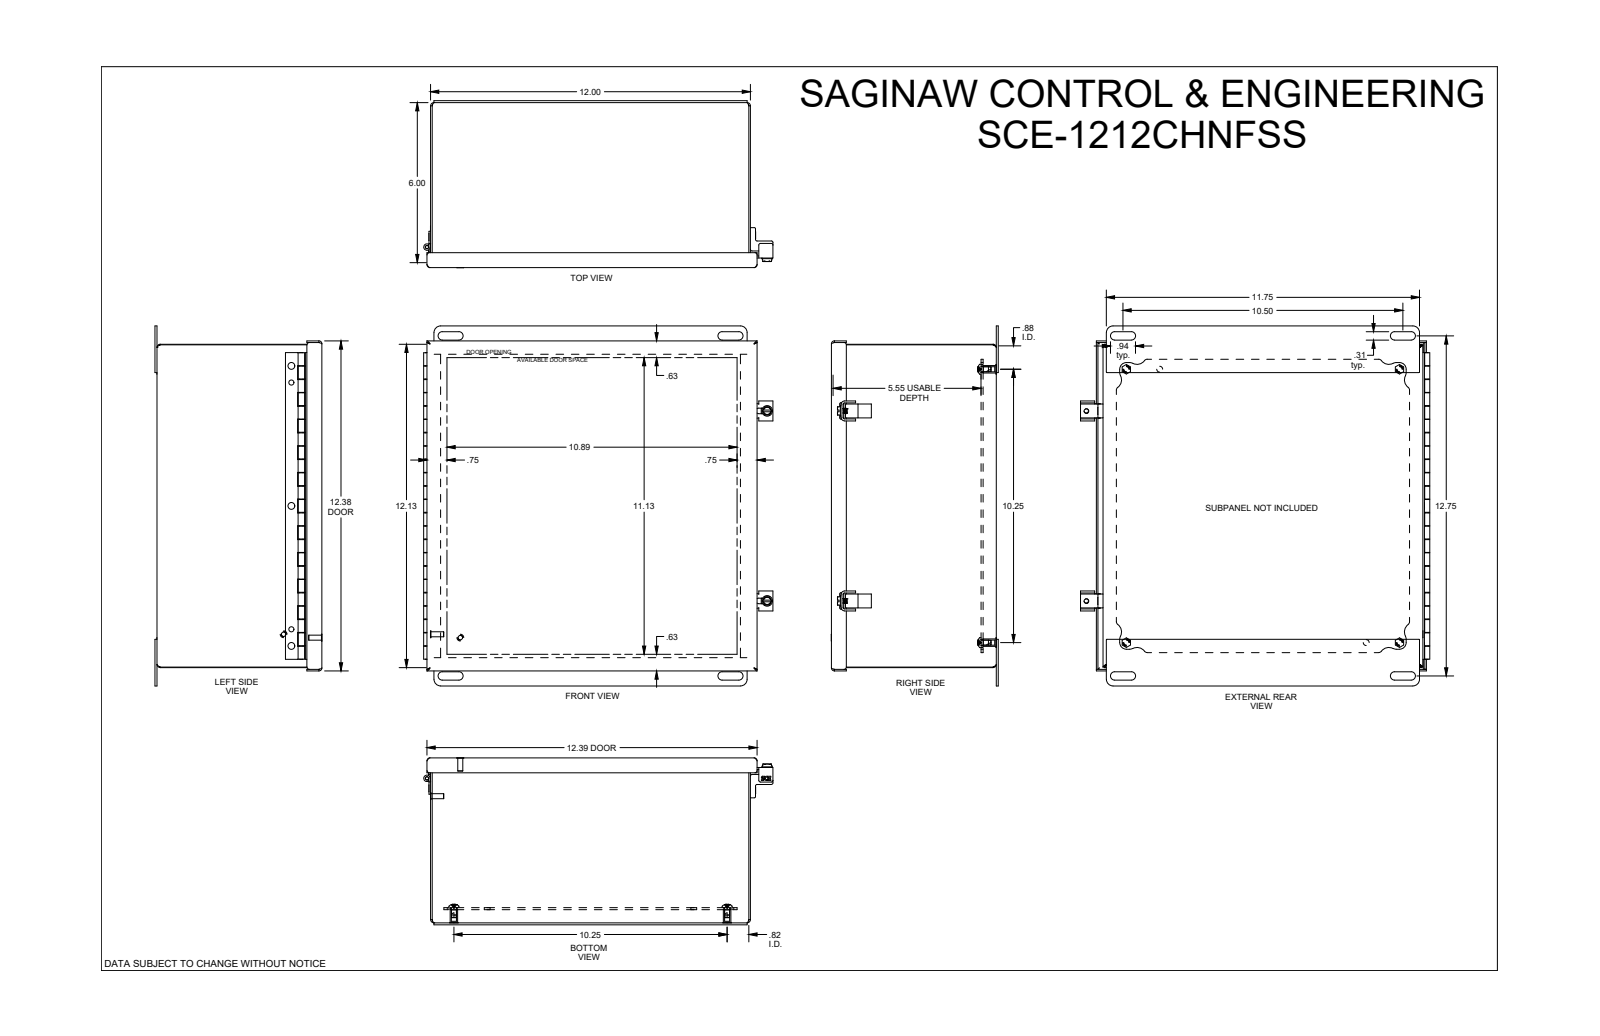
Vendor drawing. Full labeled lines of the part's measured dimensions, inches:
Part name (STEP PRODUCT): SCE-1212CHNF
STEP written by: SolidWorks 2019 (AUTOMOTIVE_DESIGN)
Units: inches
Bodies: 37 solids, 1255 faces (559 planar, 349 cylindrical, 347 other)
Overall size (bounding box): 13.5 × 13.104 × 6.265
Volume: 54.25 in³ · Surface area: 1 693 in²
Round holes (diameter × count): ⌀0.19 ×9, ⌀0.193 ×7, ⌀0.25 ×4, ⌀0.281 ×4, ⌀0.156 ×2, ⌀0.218 ×2, ⌀0.266 ×2, ⌀0.126 ×1, ⌀0.187 ×1
Round bosses / shafts (diameter × count): ⌀0.188 ×11, ⌀0.256 ×7, ⌀0.373 ×4, ⌀0.28 ×4, ⌀0.396 ×2, ⌀0.188 ×2, ⌀0.246 ×1, ⌀0.123 ×1
Partial cylindrical surfaces — rounded edges, fillets, slot ends (radius × count): R0.01 ×76, R0.06 ×33, R0.25 ×16, R0.05 ×8, R0.125 ×8, R0.156 ×8, R0.344 ×8, R0.027 ×6
Main face-to-face distances: 0.06, 6.125, 6.185, 6.065, 11.94, 12.065, 0.075, 0.51, 0.435, 5.63
Hole centre spacings: 10.249, 10.25, 11.854, 14.495, 14.496, 14.613, 13.641, 1.065
